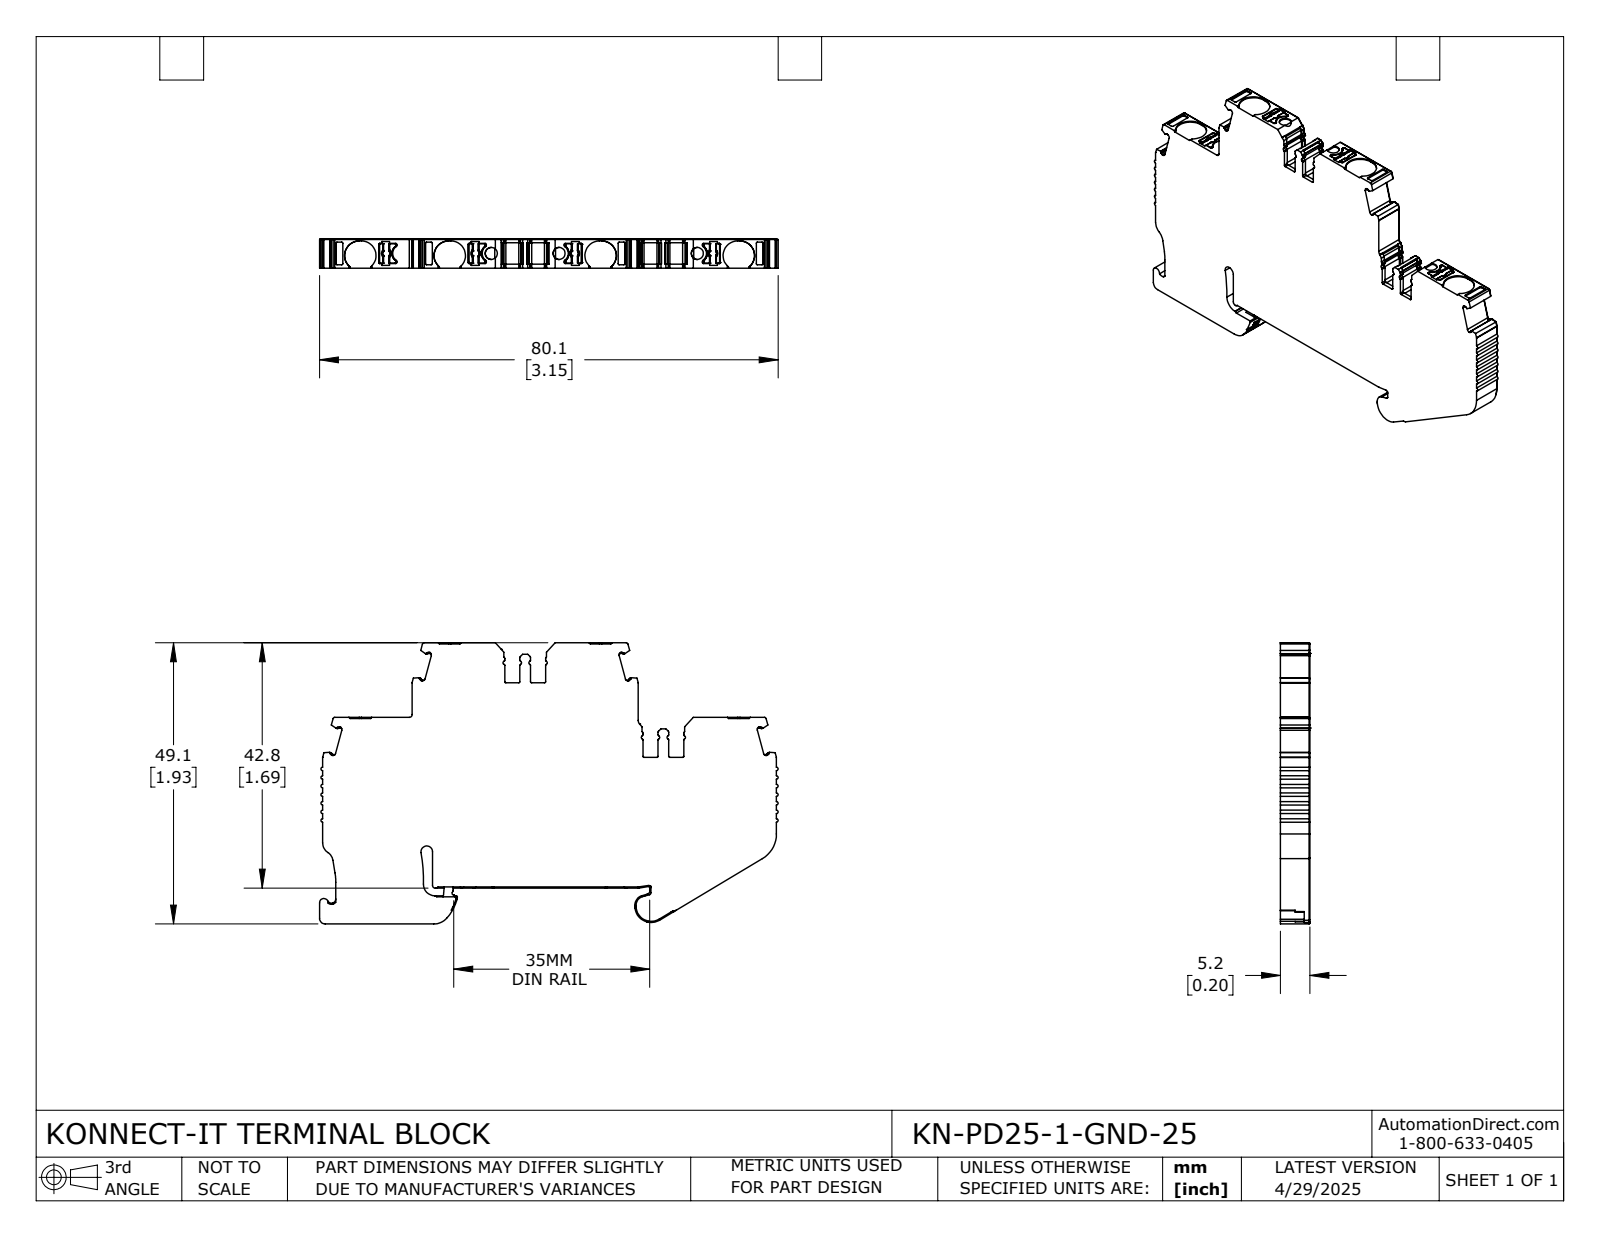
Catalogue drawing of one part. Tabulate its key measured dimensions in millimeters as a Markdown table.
| quantity | value |
| --- | --- |
| part name | KN-PD25-1-GND-25 |
| STEP written by | SolidWorks 2024 (CONFIG_CONTROL_DESIGN) |
| units | millimeters |
| bodies | 1 solid, 1035 faces (503 planar, 463 cylindrical, 69 other) |
| overall size | 80.09 × 49.09 × 5.15 |
| volume | 14 524 mm³ |
| surface area | 7 555 mm² |
| round holes (diameter × count) | 2.1 × 3 |
| partial cylindrical surfaces (radius × count) | 0.2 × 99, 0.3 × 59, 0.1 × 41, 0.4 × 25, 0.5 × 20, 0.15 × 16, 0.6 × 9, 1 × 9 |
| main face-to-face distances | 5.15, 13.01, 29.61, 42.62, 6.26, 48.88, 24.14, 35.87, 12.81, 6.46 |
| hole center spacings | 11.84, 24.14, 35.98 |
